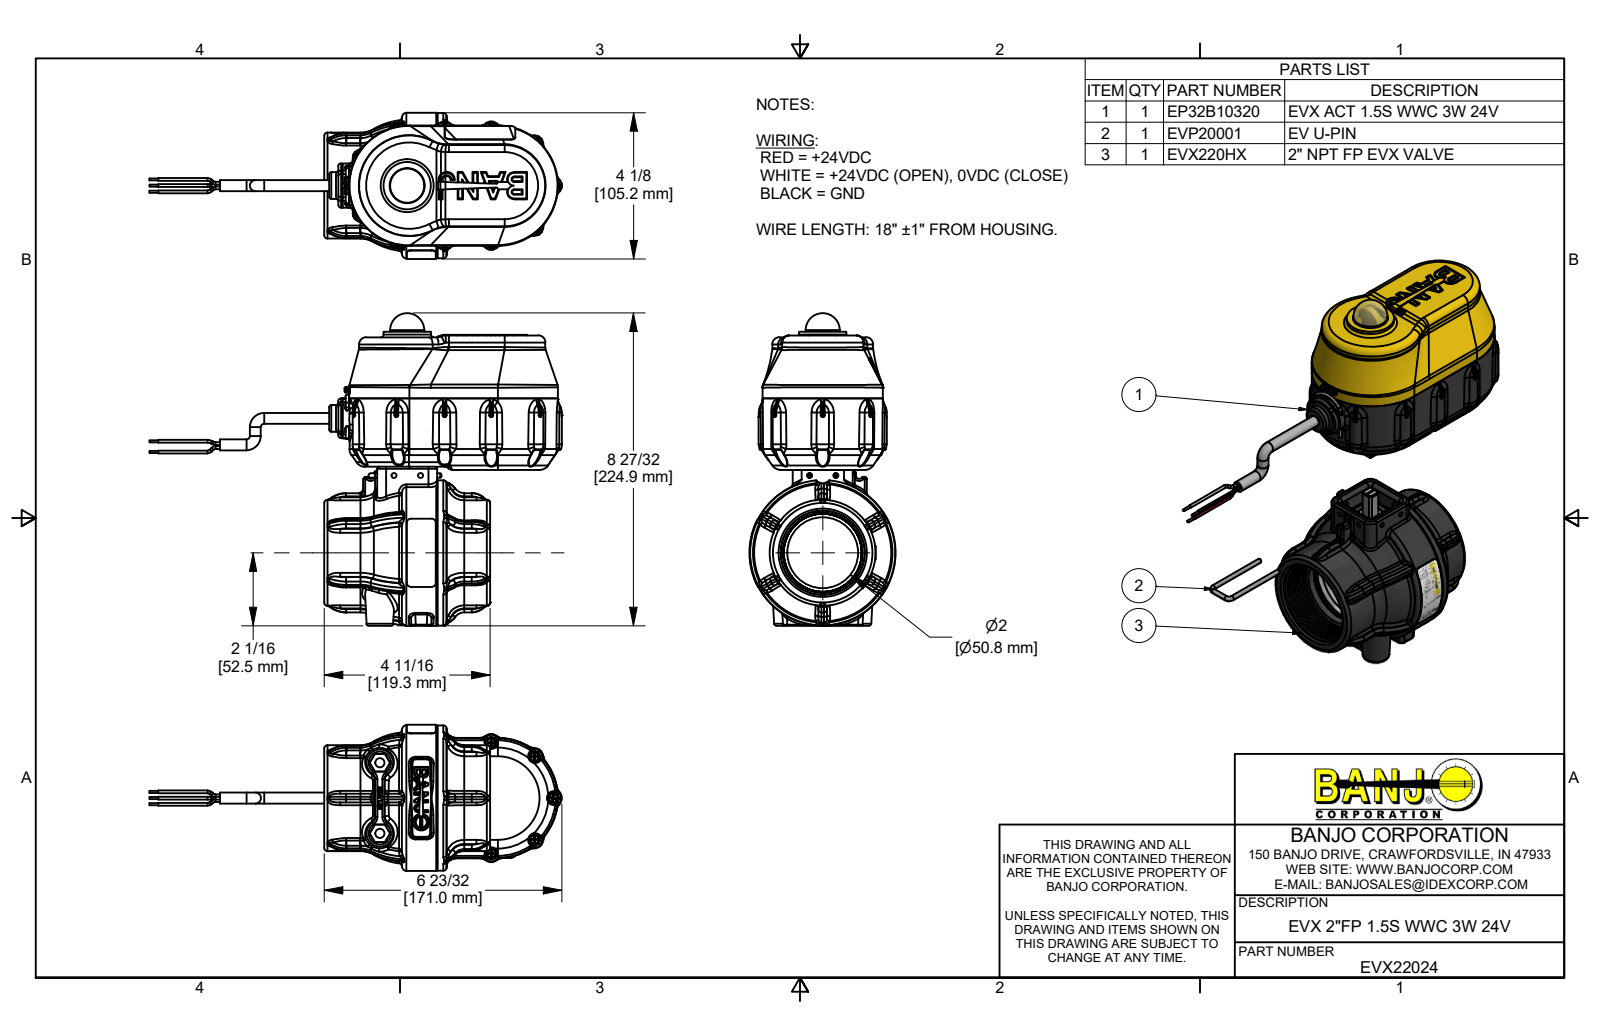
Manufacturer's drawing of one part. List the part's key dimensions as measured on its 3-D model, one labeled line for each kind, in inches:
Part name (STEP PRODUCT): EVX22024; EP32B10320; B61905PPHS; B632038PM (+8 more)
STEP written by: Autodesk Inventor 2019 (AUTOMOTIVE_DESIGN)
Units: inches
Bodies: 84 solids, 11523 faces (3120 planar, 3186 cylindrical, 5217 other)
Overall size (bounding box): 40.387 × 8.856 × 4.14
Volume: 55.97 in³ · Surface area: 901 in²
Round holes (diameter × count): ⌀0.095 ×11, ⌀0.15 ×11, ⌀0.08 ×7, ⌀0.135 ×5, ⌀0.107 ×4, ⌀0.126 ×4, ⌀0.136 ×4, ⌀0.148 ×4, ⌀0.15 ×4, ⌀0.17 ×4, ⌀0.105 ×2, ⌀0.118 ×2
Round bosses / shafts (diameter × count): ⌀0.25 ×17, ⌀0.08 ×15, ⌀0.14 ×11, ⌀0.108 ×11, ⌀0.085 ×11, ⌀0.058 ×6, ⌀0.27 ×4, ⌀0.219 ×4
Partial cylindrical surfaces — rounded edges, fillets, slot ends (radius × count): R0.013 ×180, R0.04 ×145, R0.01 ×84, R0.02 ×70, R0.09 ×56, R0.005 ×53, R0.03 ×34, R0.06 ×31
Main face-to-face distances: 0.1, 2.565, 0.211, 0.151, 0.06, 0.05, 0.569, 1.896, 1.836, 1.685
Hole centre spacings: 2.656, 1.662, 1.774, 2.219, 2.73, 2.913, 3.789, 0.487
